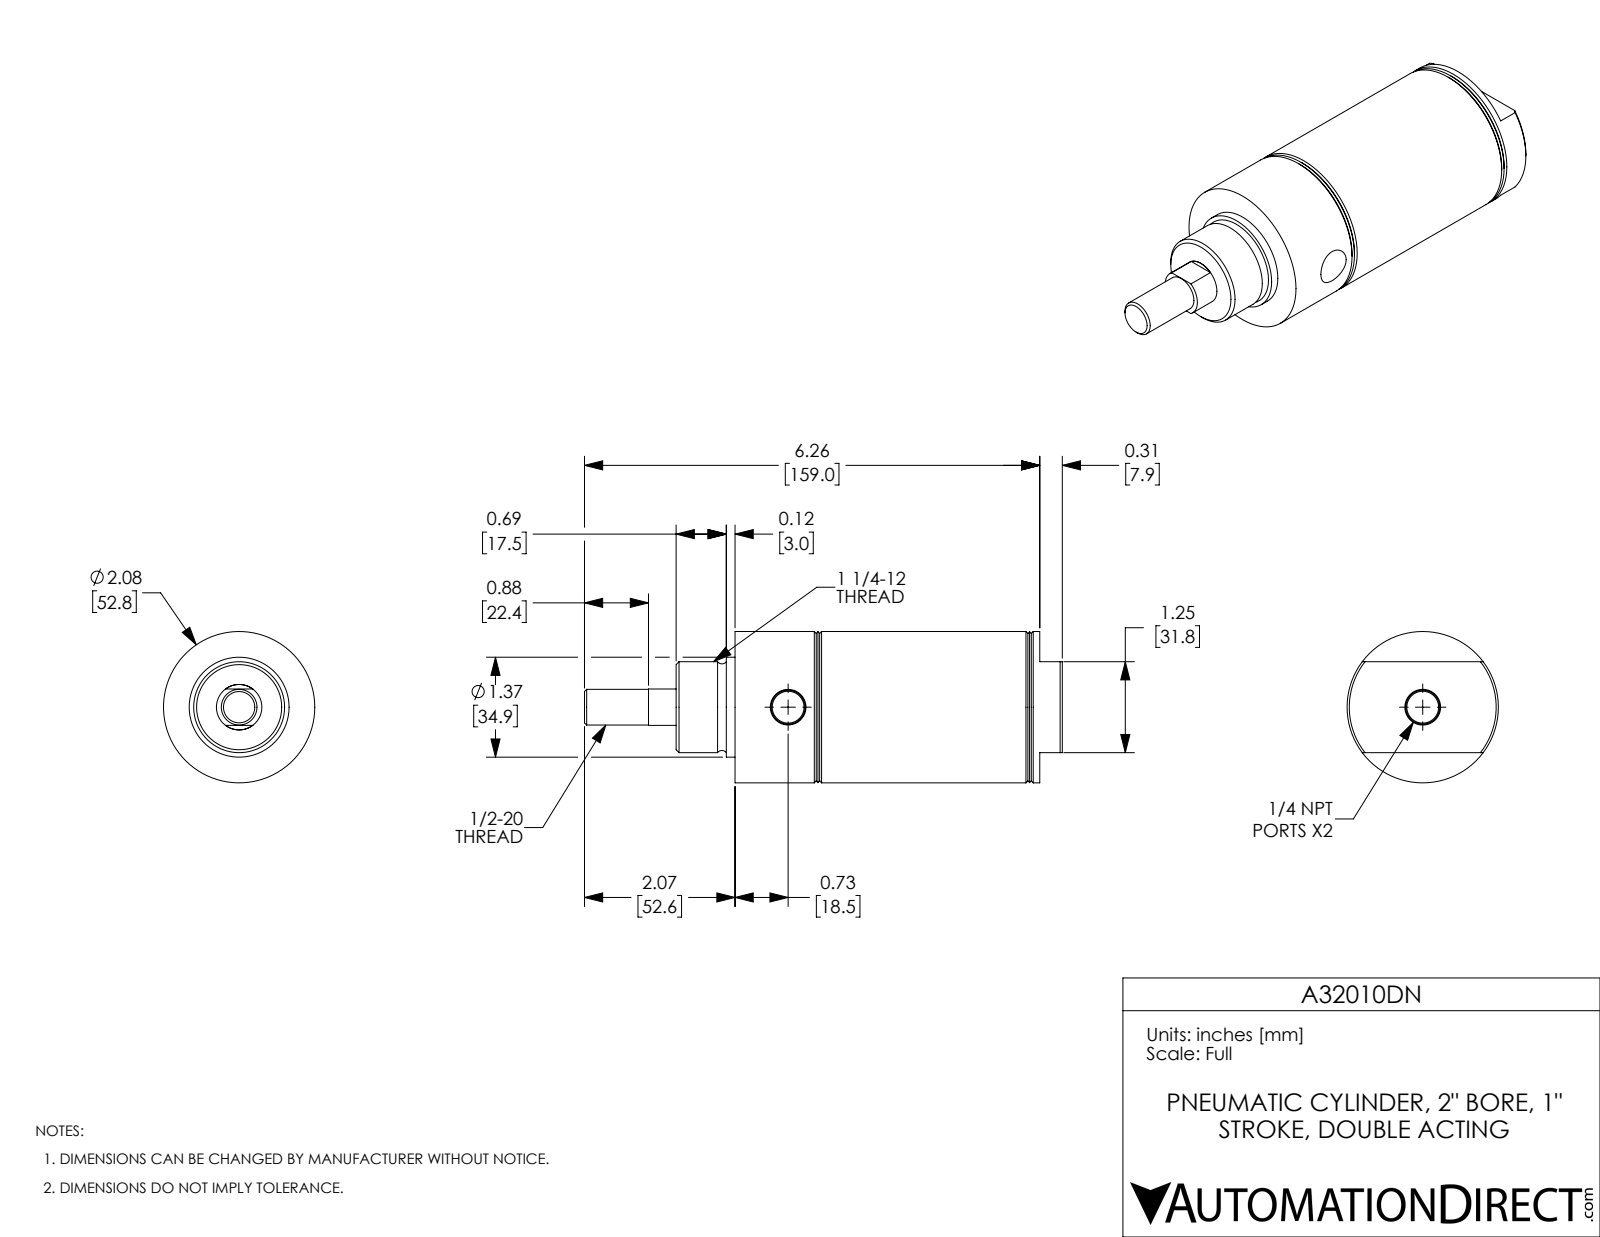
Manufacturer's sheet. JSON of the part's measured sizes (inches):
{"part_name": "A32010DN-MainBody; A32010DN-Rod; A32010DN", "step_written_by": "SolidWorks 2017 (AUTOMOTIVE_DESIGN)", "units": "inches", "bodies": {"solids": 2, "faces": 77, "planar": 20, "cylindrical": 24, "other": 33}, "overall_size": [6.57, 2.08, 2.08], "volume_in3": 13.18, "surface_area_in2": 79.05, "round_holes": [[0.438, 2], [0.625, 1], [2, 1]], "round_bosses_or_shafts": [[2.08, 1], [1.373, 1], [1.25, 1], [0.491, 1]], "face_to_face_distances": [1.5, 3, 0.5, 1, 2, 4.5, 2.5, 0.31, 1.19, 1.69]}
